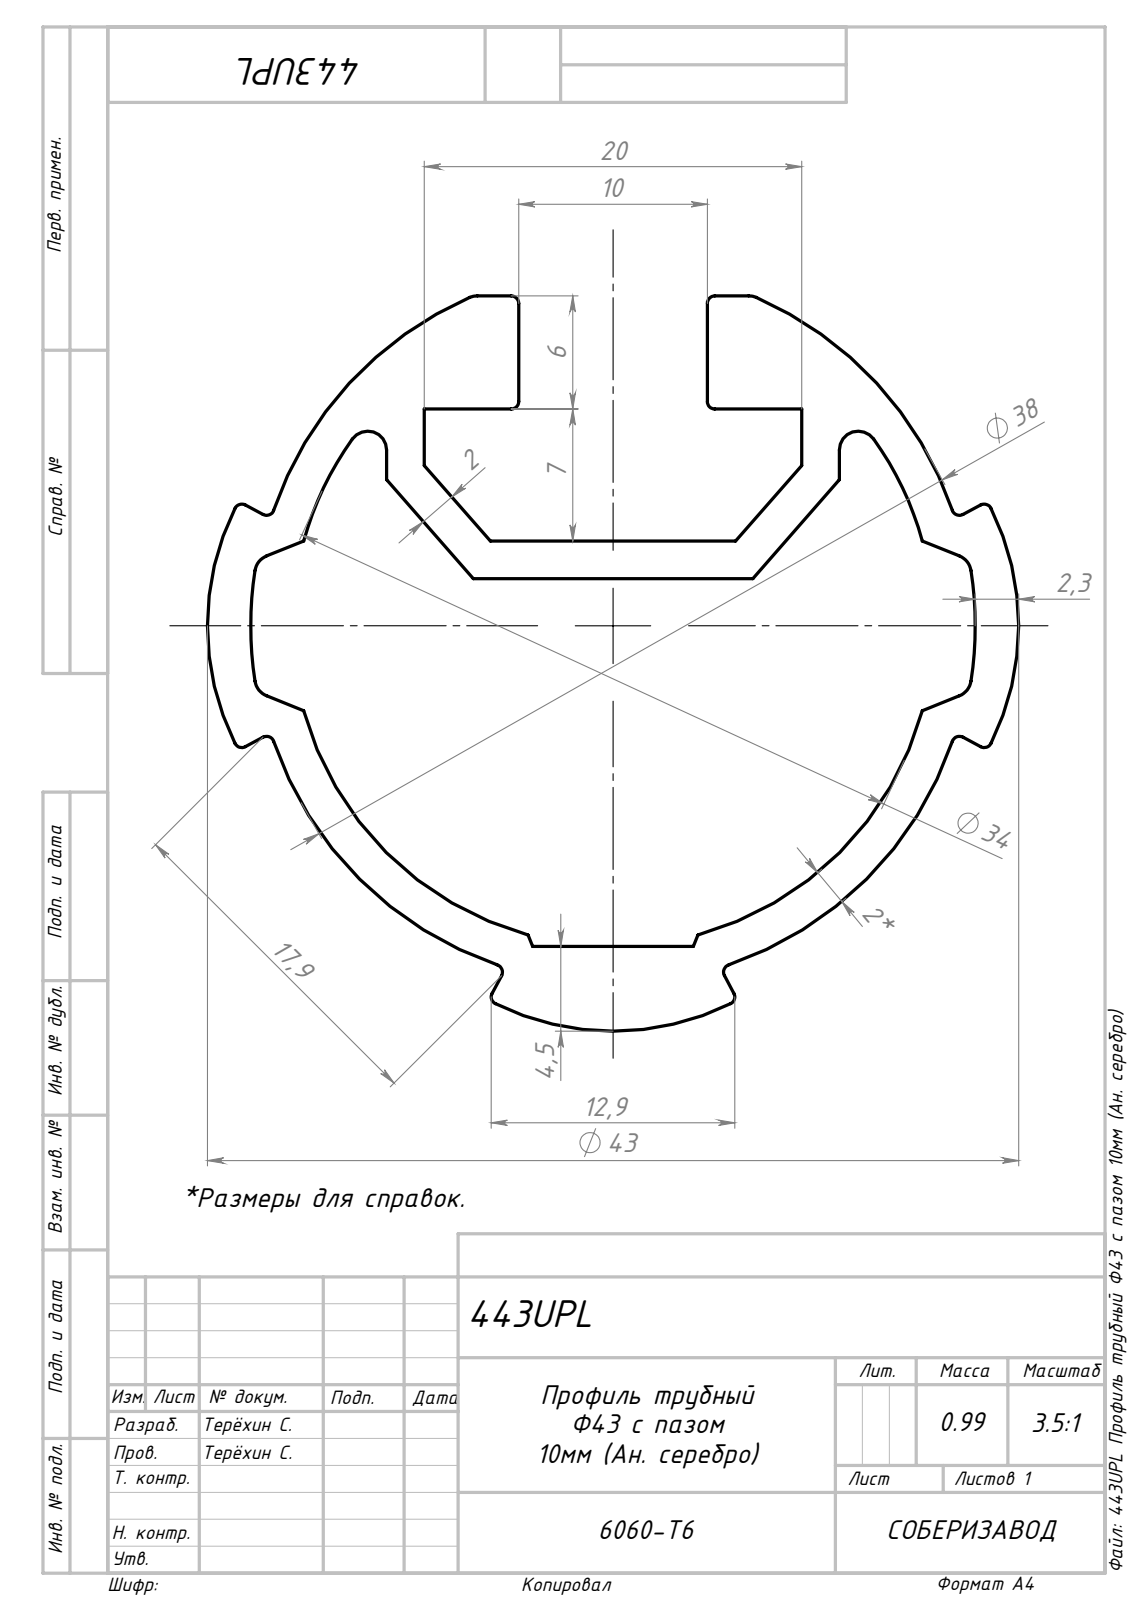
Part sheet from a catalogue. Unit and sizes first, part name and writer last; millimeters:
Units: millimetres
Overall size (bounding box): 1000 × 43 × 39
Partial cylindrical surfaces — rounded edges, fillets, slot ends (radius × count): R0.4 ×16, R1 ×8, R14 ×3, R17 ×1, R19 ×1, R19.2 ×1
Main face-to-face distances: 2, 7, 15, 9, 19.5, 21.5, 28.5, 5, 10, 20.58
Volume: 365 950 mm³ · Surface area: 294 751 mm²
Bodies: 1 solid, 72 faces (31 planar, 41 cylindrical, 0 other)
Part name (STEP PRODUCT): Сборка9; 443UPL Профиль трубный Φ43 с пазом 10мм (Ан. серебро)_00
STEP written by: SolidWorks 2022 (AUTOMOTIVE_DESIGN)
